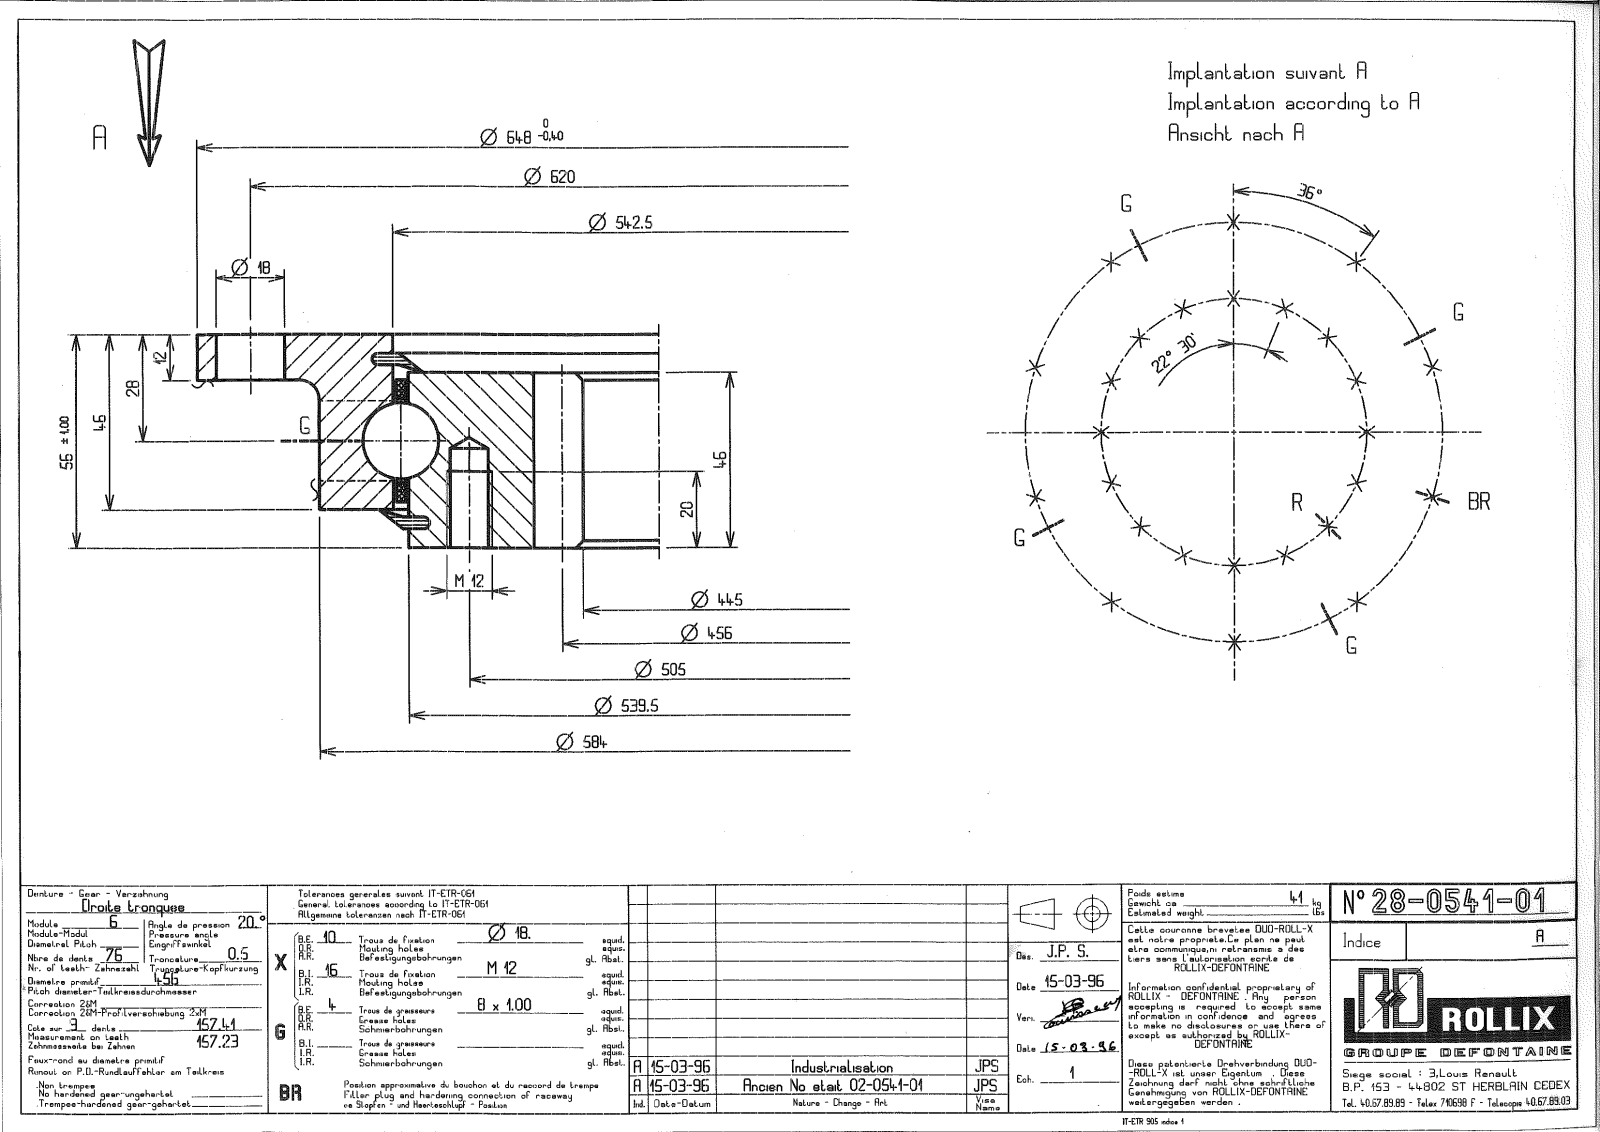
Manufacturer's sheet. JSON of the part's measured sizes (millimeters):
{"part_name": "22-0541-01", "step_written_by": "SolidWorks 2016 (CONFIG_CONTROL_DESIGN)", "units": "millimeters", "bodies": {"solids": 9, "faces": 697, "planar": 205, "cylindrical": 238, "other": 254}, "overall_size": [648, 648, 56], "volume_mm3": 4802000, "surface_area_mm2": 857268, "round_holes": [[10.25, 16], [18, 10], [7, 4], [545.5, 1]], "round_bosses_or_shafts": [[8, 4], [648, 1], [584, 1], [536.5, 1]], "partial_cylinders_radius": [[222.5, 1], [235.5, 1]], "face_to_face_distances": [10, 46, 56, 44, 2, 12, 34, 36, 8.05, 47.95], "hole_center_spacings": [98.52, 280.56, 419.89, 193.25, 252.5, 357.09, 310, 589.66]}
